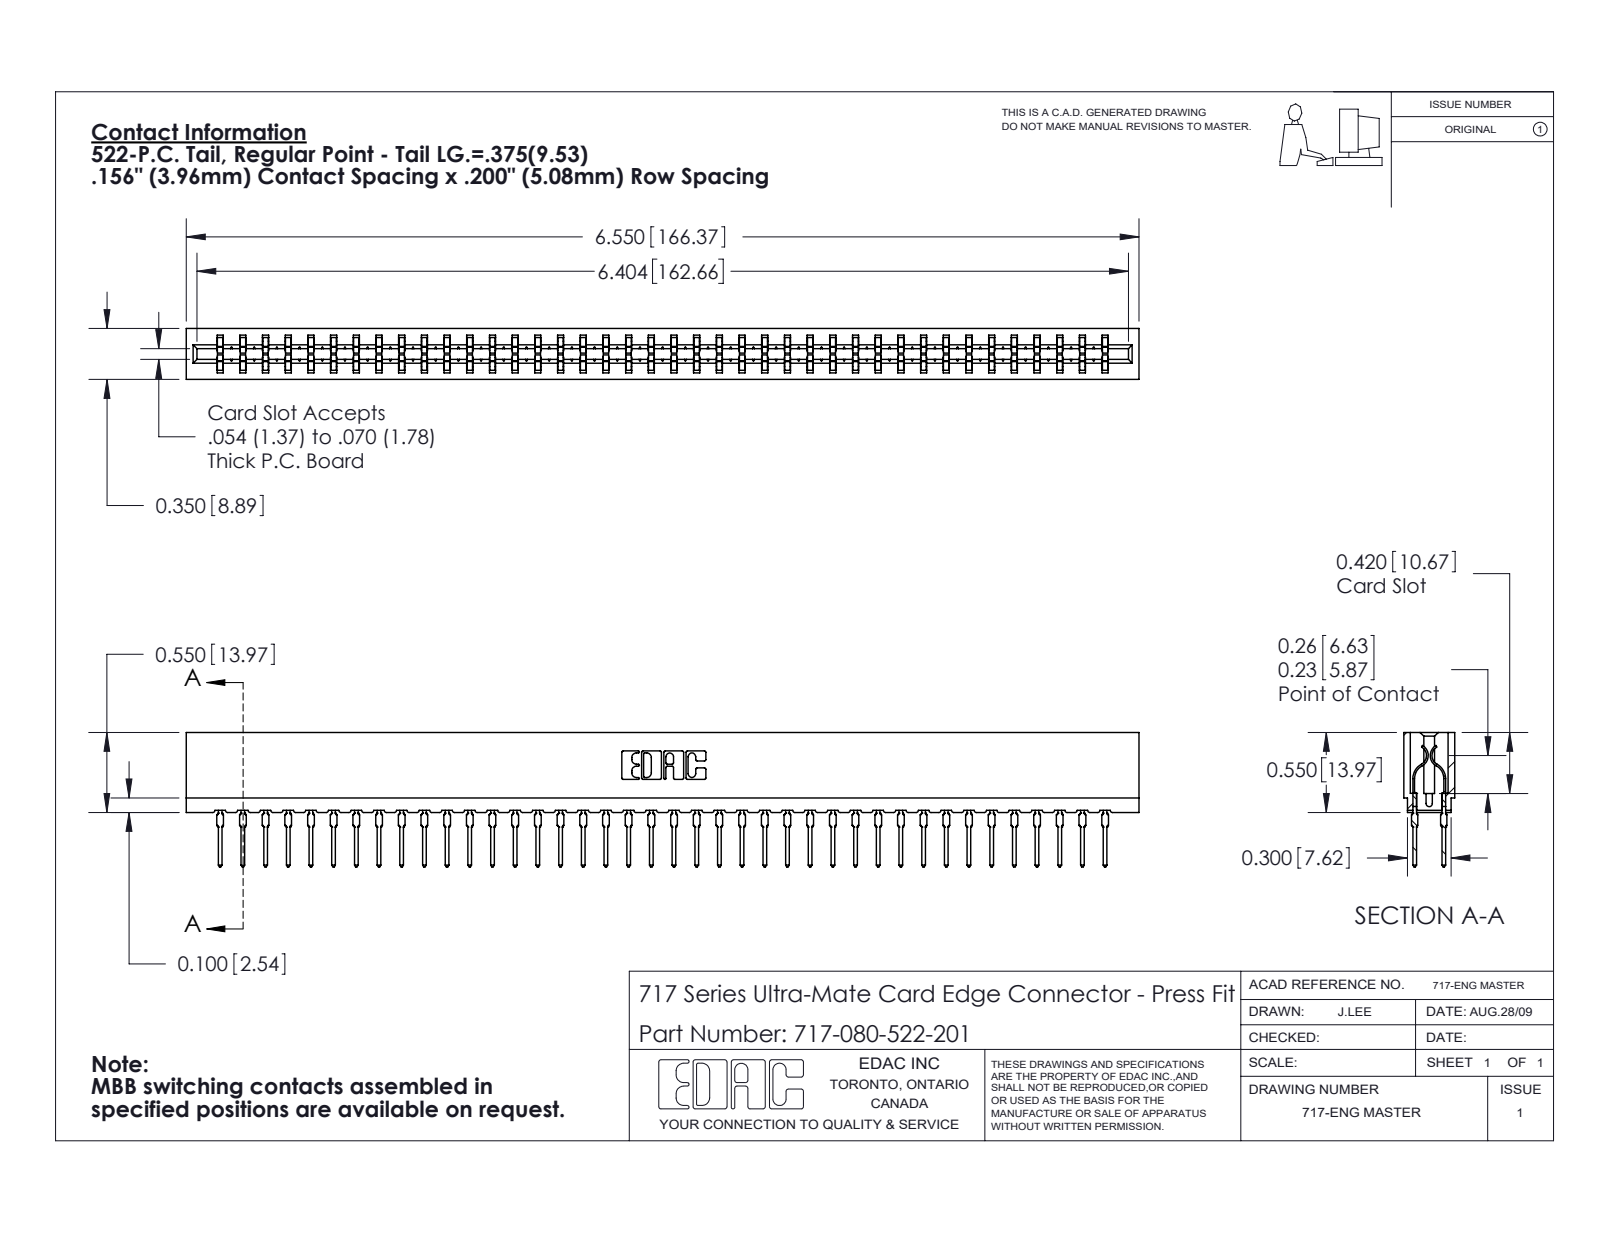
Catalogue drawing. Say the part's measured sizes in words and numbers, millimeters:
The part is named "717-080-522-201; 717 Part_Insulator Option - 06; 745-292-001_522". Its 3-D file was written by "SolidWorks 2020 (CONFIG_CONTROL_DESIGN)". It is 81 solids with 7294 faces: 3774 planar, 1440 cylindrical and 2080 other. Overall it measures 166.4 by 23.5 by 8.9 millimeters. Its volume is 14 500 cubic millimeters and its surface area 22 480 square millimeters. Partial cylindrical surfaces (rounded edges, fillets, slot ends): 160 of radius 0.5, 80 of radius 0.4, 22 of radius 0.3, 8 of radius 0.1, 8 of radius 0.3, 6 of radius 0.2, 6 of radius 0.8, 3 of radius 0.7. The main face-to-face distances are 5.4, 3.5, 8.9, 1.6, 7.3, 1.9, 3.8, 1.9, 1.1, 7.7.
